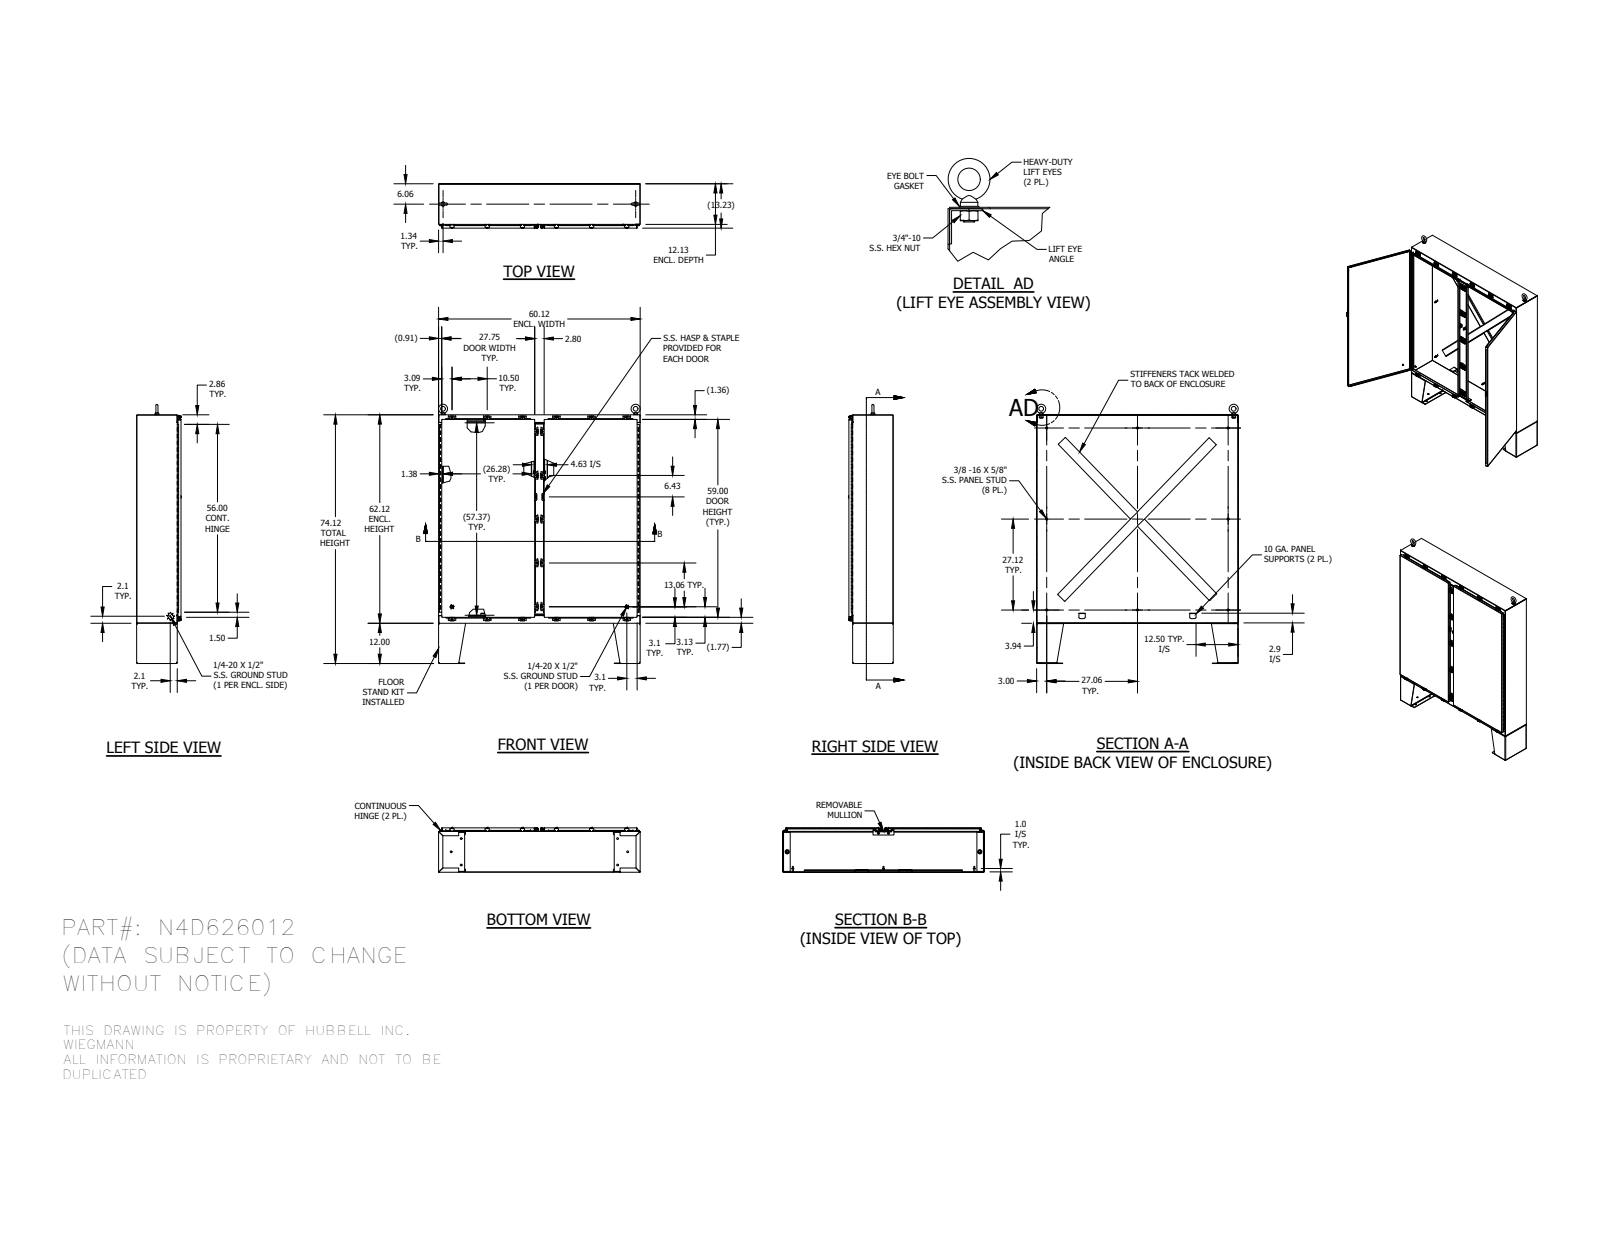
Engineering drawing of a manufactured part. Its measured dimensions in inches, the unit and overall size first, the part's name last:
Units: inches
Overall size (bounding box): 77.248 × 60.125 × 13.355
Round holes (diameter × count): ⌀0.11 ×44, ⌀0.211 ×22, ⌀0.281 ×22, ⌀0.3 ×22, ⌀0.563 ×18, ⌀0.375 ×16, ⌀0.196 ×4, ⌀0.201 ×4, ⌀0.312 ×4, ⌀0.313 ×4, ⌀0.142 ×2, ⌀0.156 ×2
Round bosses / shafts (diameter × count): ⌀0.25 ×29, ⌀0.52 ×22, ⌀0.5 ×22, ⌀0.35 ×22, ⌀0.33 ×10, ⌀0.625 ×8, ⌀0.438 ×4, ⌀0.337 ×3
Partial cylindrical surfaces — rounded edges, fillets, slot ends (radius × count): R0.03 ×246, R0.125 ×54, R0.141 ×44, R0.25 ×37, R0.062 ×32, R0.094 ×22, R0.1 ×22, R0.219 ×22
Main face-to-face distances: 0.094, 13.133, 13.039, 13.227, 12.031, 1.102, 60.031, 62.031, 0.125, 12.125
Hole centre spacings: 10.5, 60.633, 30.315, 0.876, 9.693, 11.317, 31.125, 59.717
Volume: 1 285 in³ · Surface area: 27 059 in²
Bodies: 175 solids, 6460 faces (2572 planar, 2576 cylindrical, 1312 other)
Part name (STEP PRODUCT): FK1212_1; 38412_1; FK1212LG_1; 30824-4_1 (+8 more)
STEP written by: SolidWorks 2014 (AUTOMOTIVE_DESIGN)
